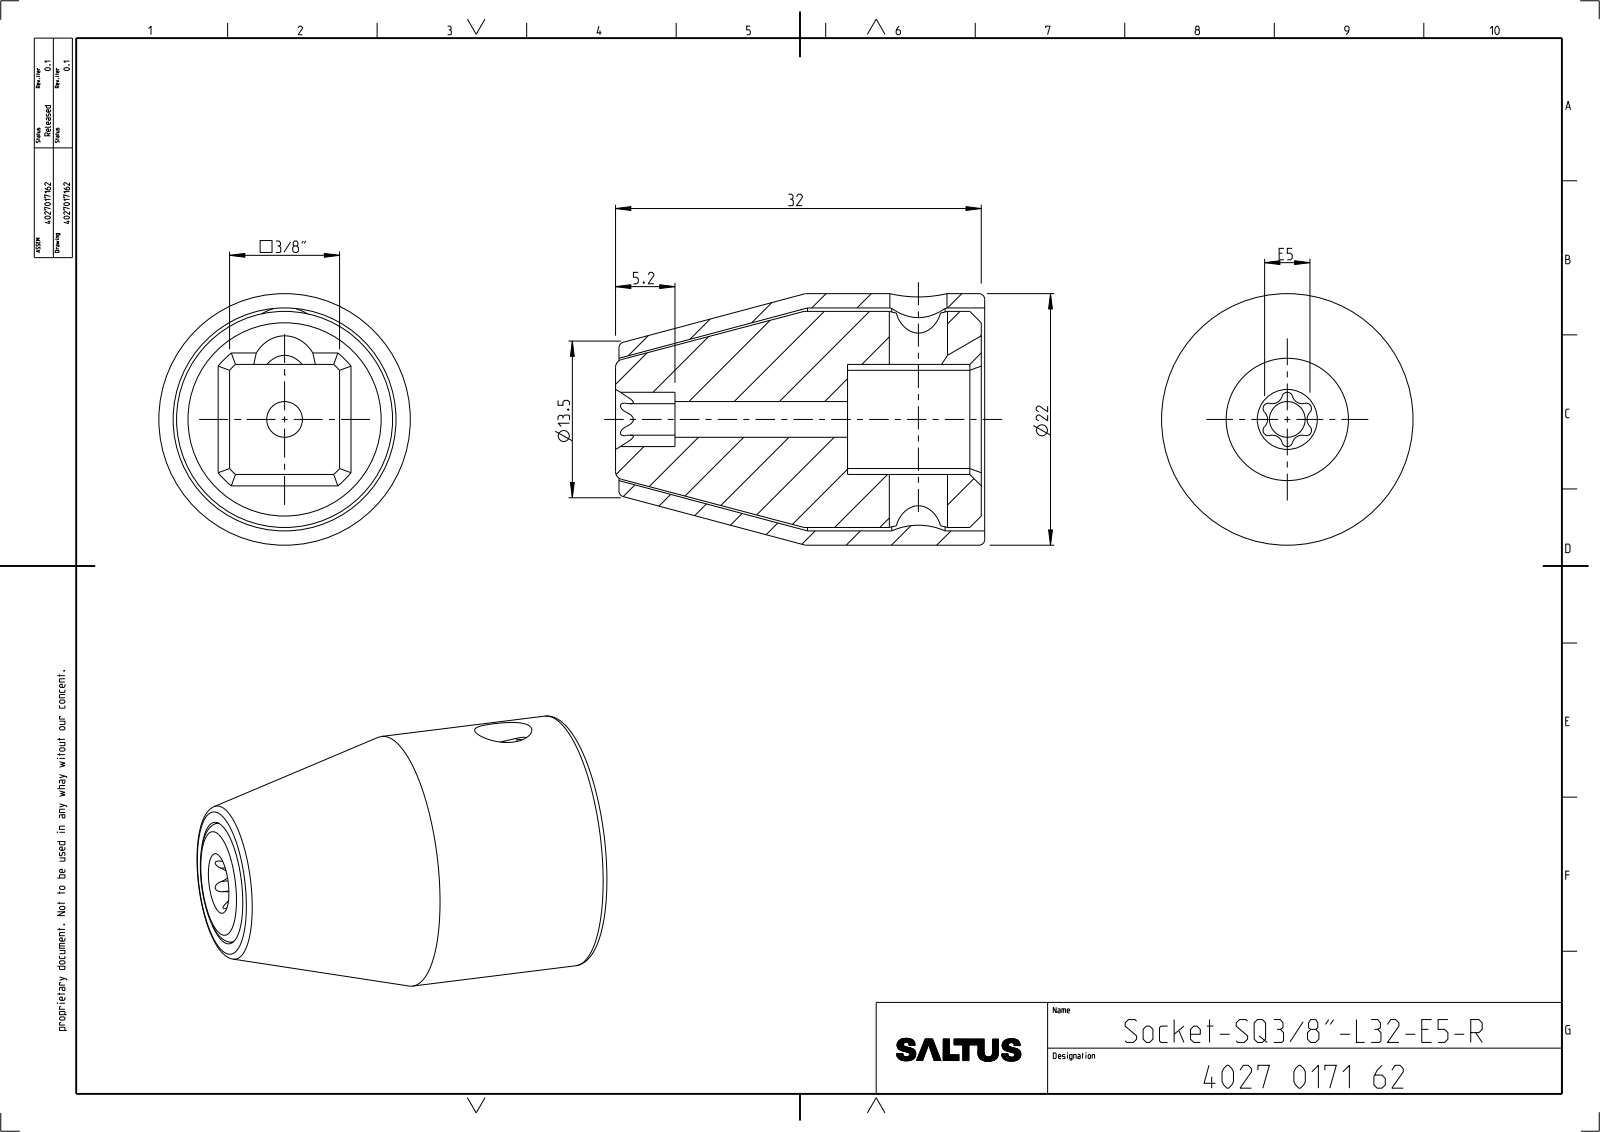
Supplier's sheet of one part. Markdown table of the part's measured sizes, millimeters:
| quantity | value |
| --- | --- |
| part name | 4027122005; 4027039634; 4027017162_ASM |
| STEP written by | CREO PARAMETRIC BY PTC INC, 2022414 (CONFIG_CONTROL_DESIGN) |
| units | millimeters |
| bodies | 2 solids, 73 faces (15 planar, 35 cylindrical, 23 other) |
| overall size | 32.3 × 22 × 22 |
| volume | 7 888 mm³ |
| surface area | 6 595 mm² |
| round holes (diameter × count) | 3.12 × 1, 5 × 1, 5.09 × 1, 19.5 × 1 |
| round bosses / shafts (diameter × count) | 22 × 1, 18.9 × 1 |
| partial cylindrical surfaces (radius × count) | 0.47 × 6, 0.88 × 6, 3 × 1, 6.45 × 1 |
| main face-to-face distances | 9.62, 11.7, 32, 12, 32.3, 20.3, 31.7, 20, 27.1, 26.8 |
